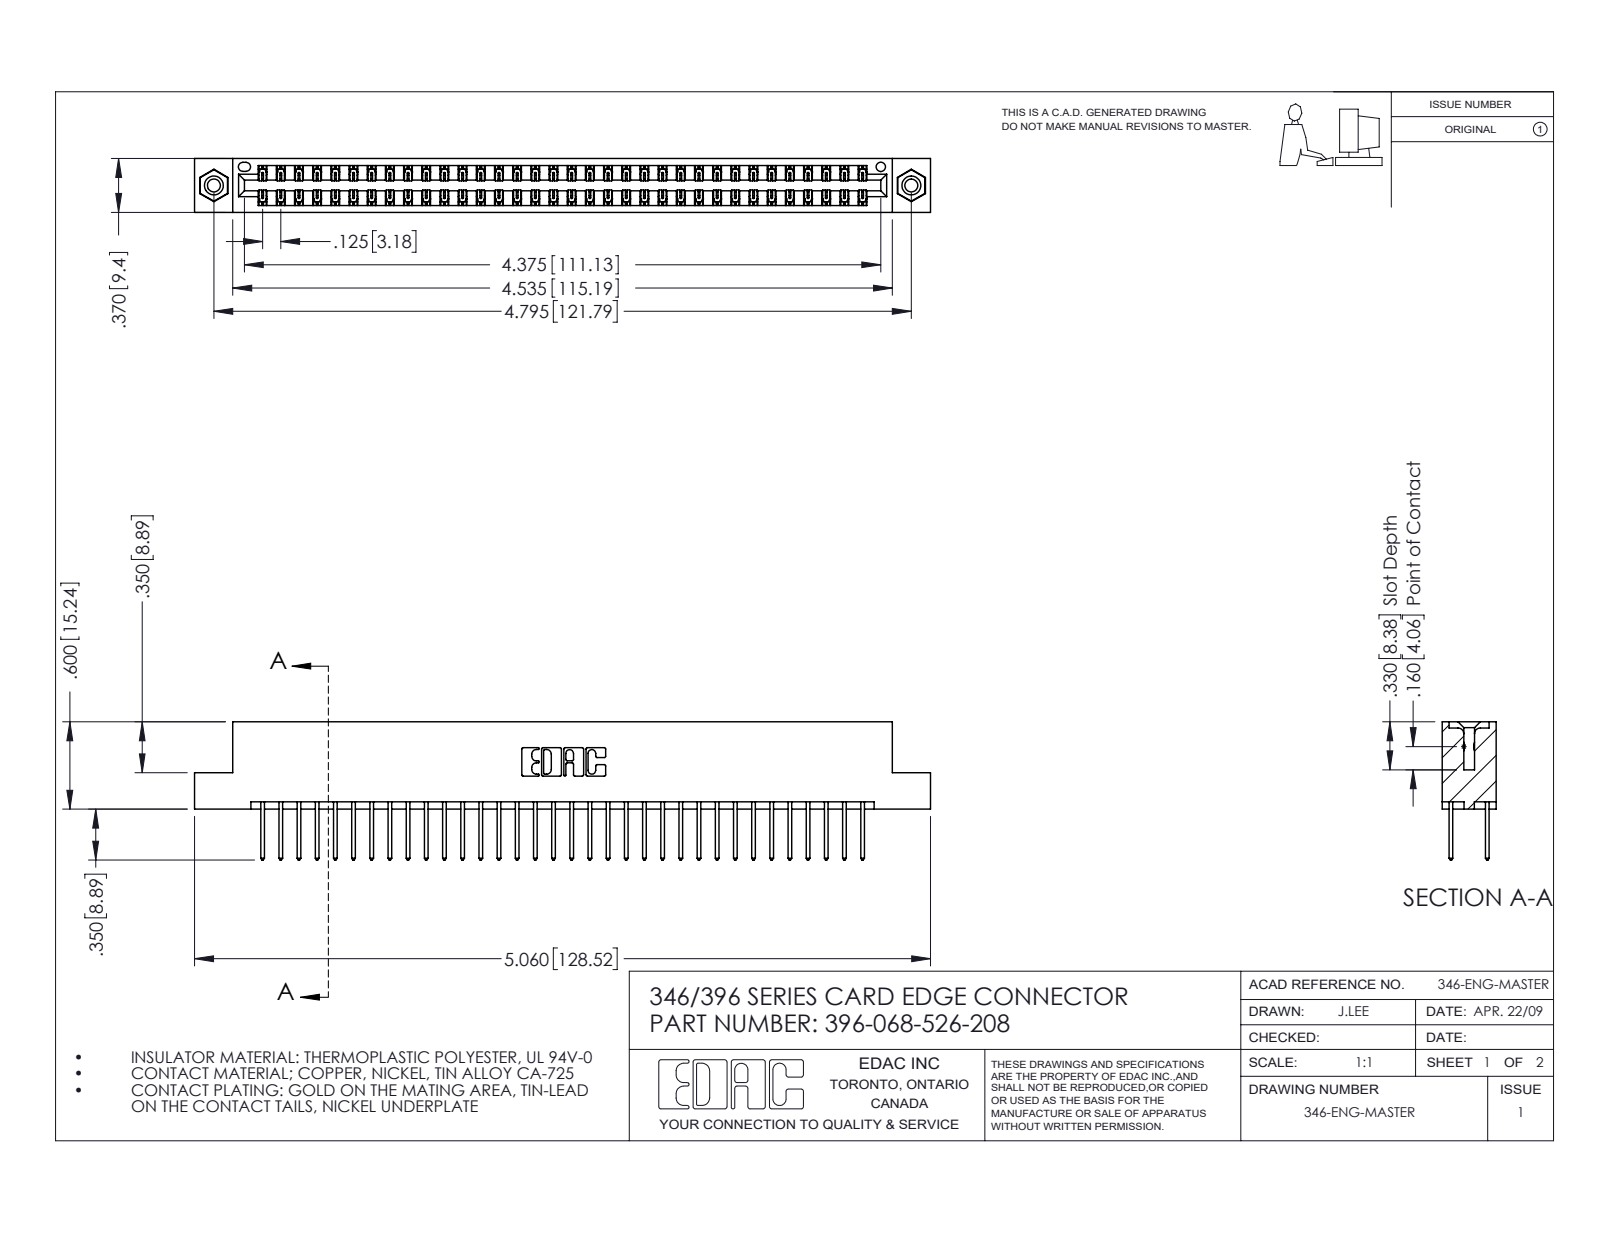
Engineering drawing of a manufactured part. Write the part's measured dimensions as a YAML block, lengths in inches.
part_name: "396-068-526-208; 345-250-001_345-250-003-102; 346 Part_Flush Mounting Lugs - 0.156 Dia-TI; 345-292-001_345-293-126"
step_written_by: "SolidWorks 2016 (CONFIG_CONTROL_DESIGN)"
units: inches
bodies: {solids: 71, faces: 3718, planar: 2488, cylindrical: 1214, other: 16}
overall_size: [5.06, 0.95, 0.37]
volume: 0.767
surface_area: 27.4
round_holes:
  - {diameter: 0.089, count: 2}
  - {diameter: 0.125, count: 2}
  - {diameter: 0.156, count: 2}
  - {diameter: 0.064, count: 1}
round_bosses_or_shafts:
  - {diameter: 0.155, count: 2}
partial_cylinders:
  - {radius: 0.006, count: 102}
  - {radius: 0.01, count: 68}
  - {radius: 0.01, count: 22}
  - {radius: 0.007, count: 6}
  - {radius: 0.031, count: 6}
  - {radius: 0.026, count: 3}
  - {radius: 0.014, count: 2}
  - {radius: 0.022, count: 2}
face_to_face_distances: [0.048, 0.322, 0.25, 0.37, 0.072, 0.298, 0.025, 0.275, 0.148, 0.222]
hole_center_spacings: [0.246, 4.587, 4.795]
